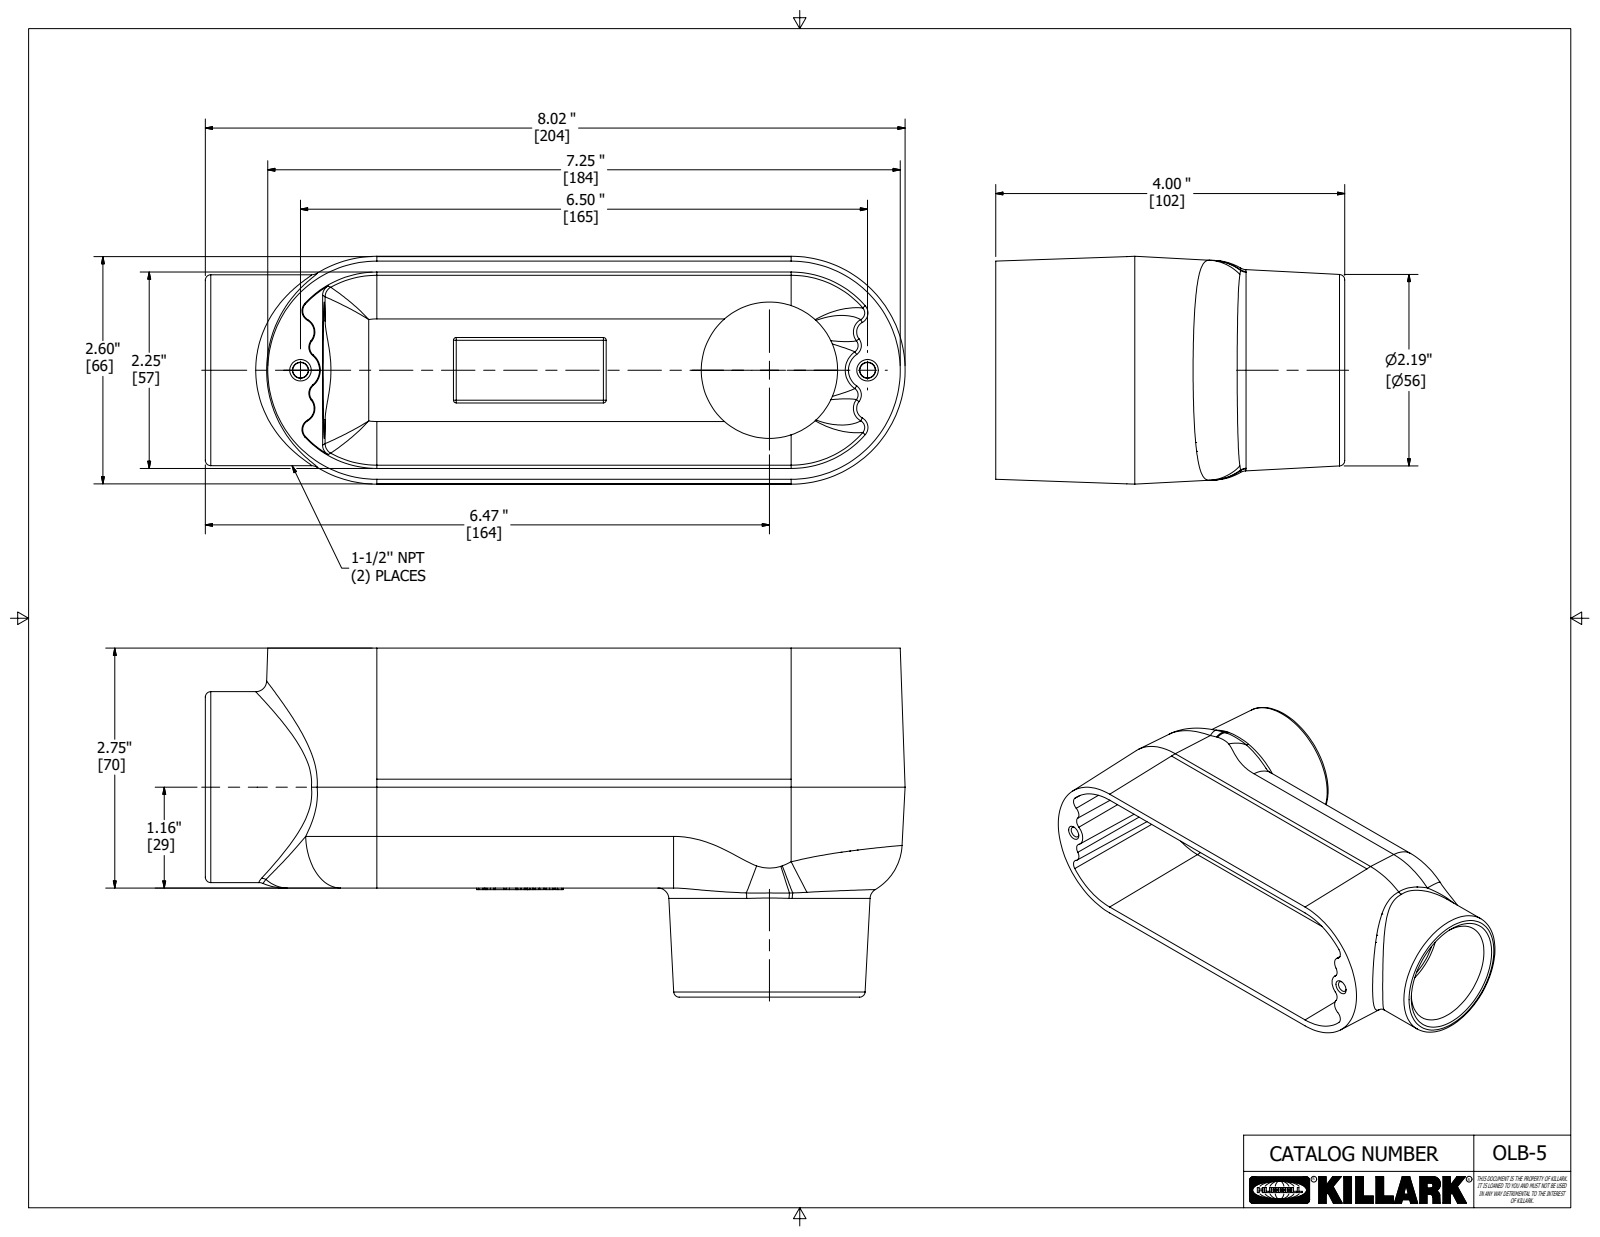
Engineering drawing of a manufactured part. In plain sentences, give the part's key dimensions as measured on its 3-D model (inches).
The part is named "17174-1". Its 3-D file was written by "Autodesk Inventor 2018 (AUTOMOTIVE_DESIGN)". It is 1 solid with 356 faces: 157 planar, 8 cylindrical and 191 other. Overall it measures 8.022 by 4 by 2.611 inches. Its volume is 14.15 cubic inches and its surface area 138.3 square inches. Round holes: 2 of diameter 1.563. Round bosses or shafts: 1 of diameter 2.187. Partial cylindrical surfaces (rounded edges, fillets, slot ends): 3 of radius 0.5, 2 of radius 0.625. The main face-to-face distances are 0.125, 2.75, 2.625, 0.031, 0.156, 2.594, 0.094, 2.719, 1.25, 1.281.
